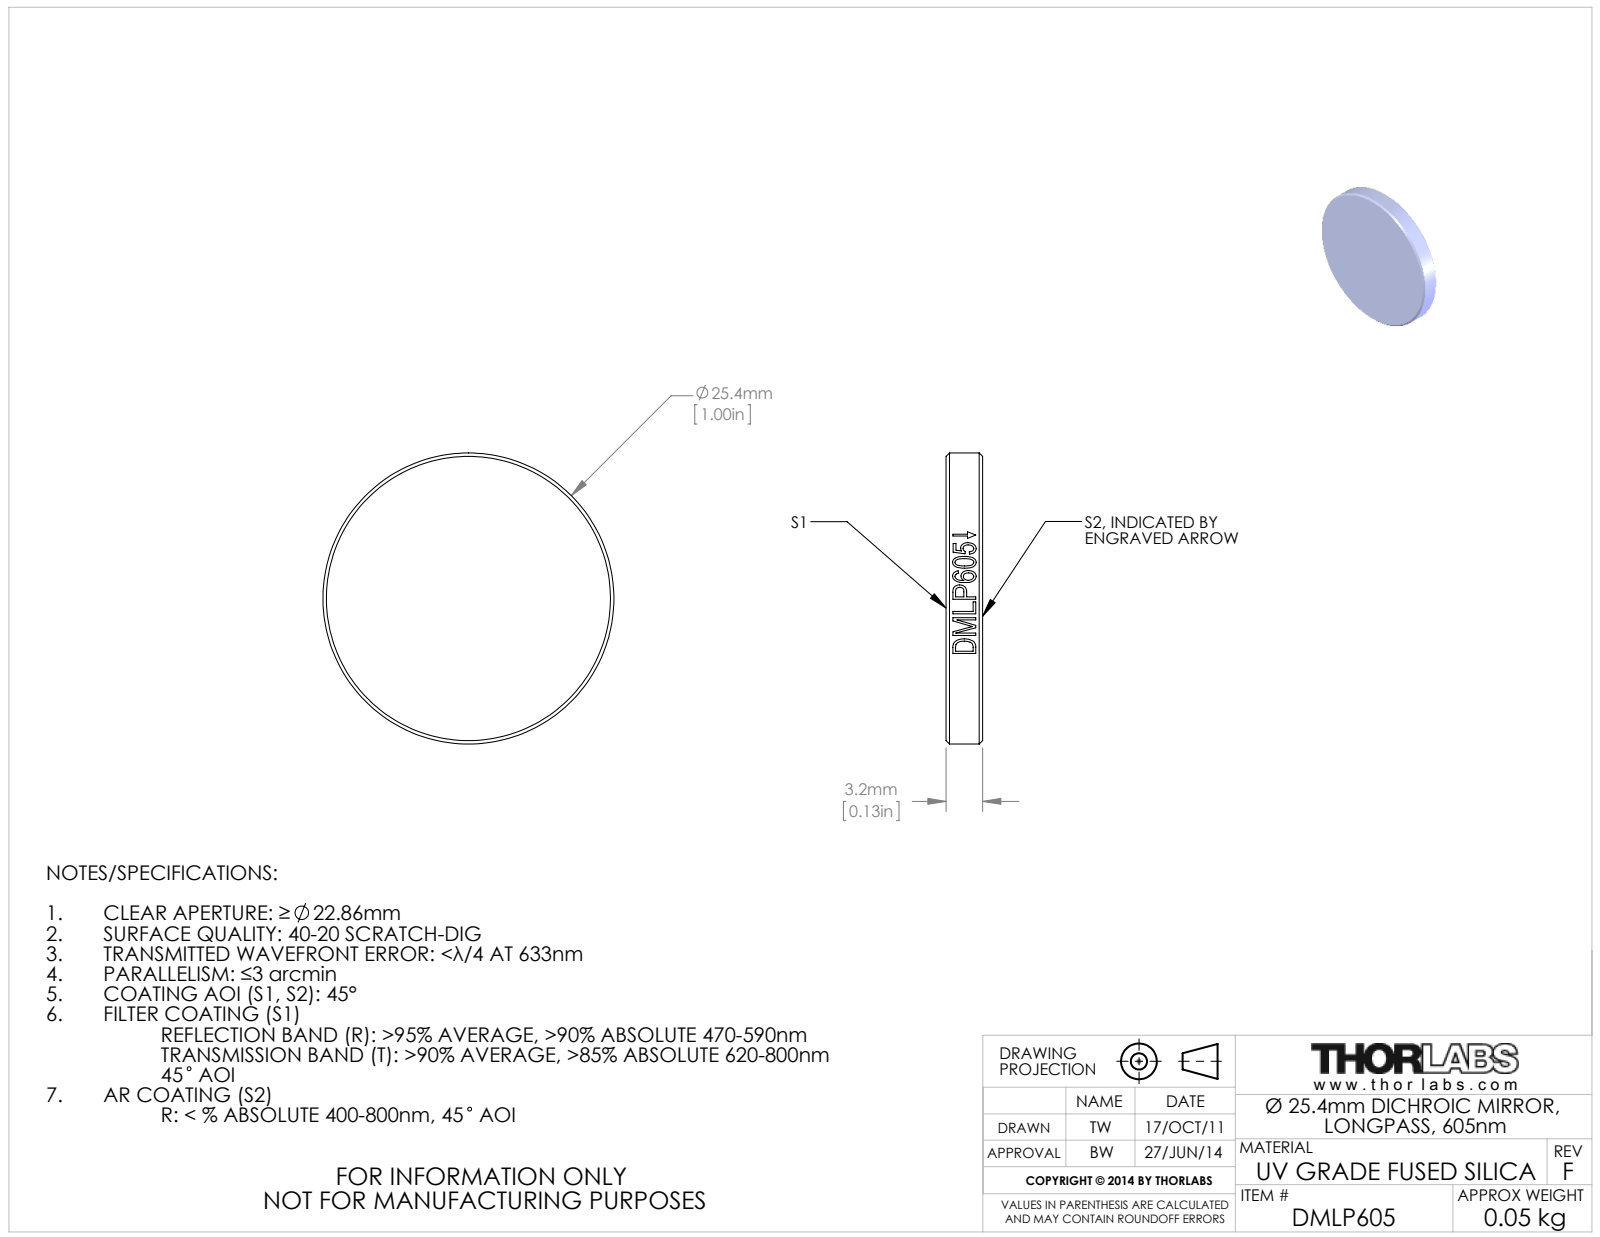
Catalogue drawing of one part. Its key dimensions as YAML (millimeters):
part_name: "18097-E0W"
step_written_by: "SolidWorks 2011 (CONFIG_CONTROL_DESIGN)"
units: millimeters
bodies: {solids: 0, faces: 20, planar: 2, cylindrical: 14, other: 4}
overall_size: [25.4, 25.4, 3.2]
round_bosses_or_shafts:
  - {diameter: 25.4, count: 1}
face_to_face_distances: [3.2]
